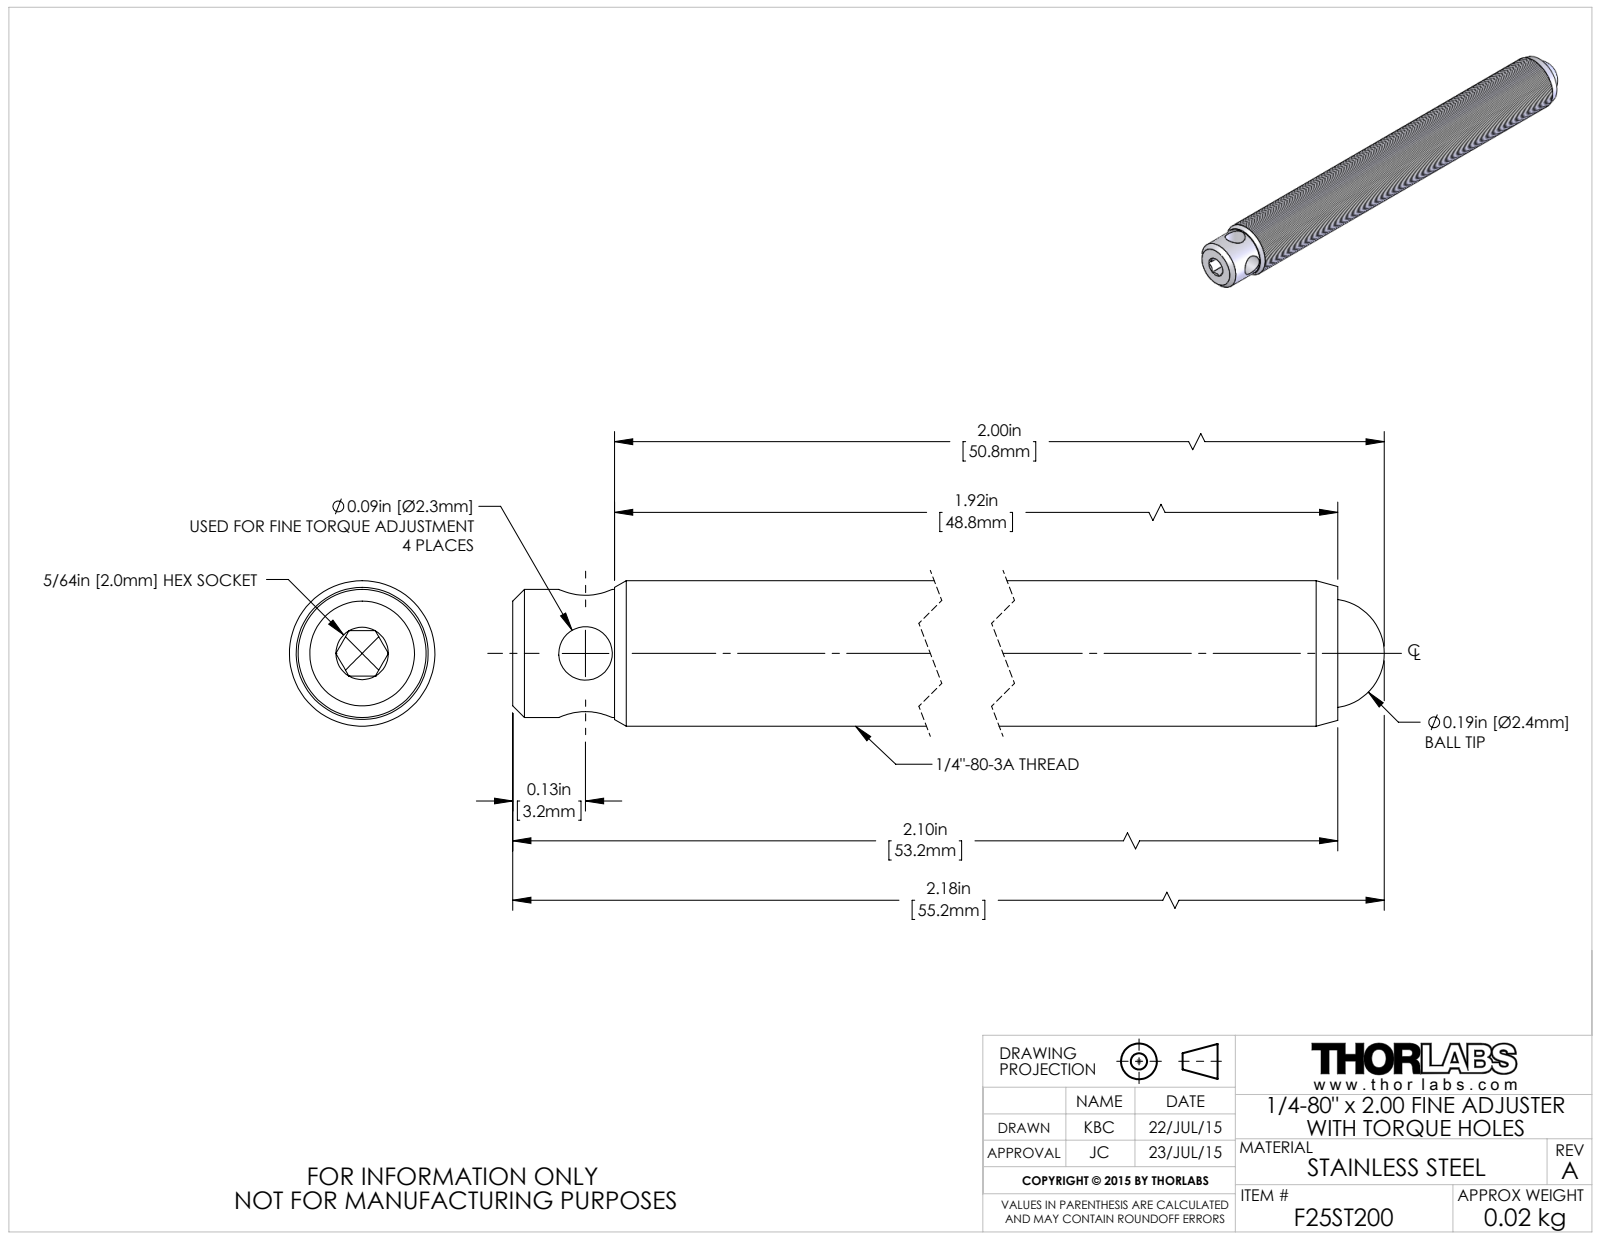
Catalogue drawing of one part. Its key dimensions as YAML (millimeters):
part_name: "TTN045072-E0W"
step_written_by: "SolidWorks 2014 (AUTOMOTIVE_DESIGN)"
units: millimeters
bodies: {solids: 2, faces: 40, planar: 9, cylindrical: 14, other: 17}
overall_size: [55.2, 6.4, 6.4]
volume: 1600
surface_area: 1244
round_holes:
  - {diameter: 2.3, count: 2}
  - {diameter: 4.8, count: 1}
round_bosses_or_shafts:
  - {diameter: 6.4, count: 1}
  - {diameter: 5.6, count: 1}
face_to_face_distances: [53.2, 2, 4.4, 48.8]
